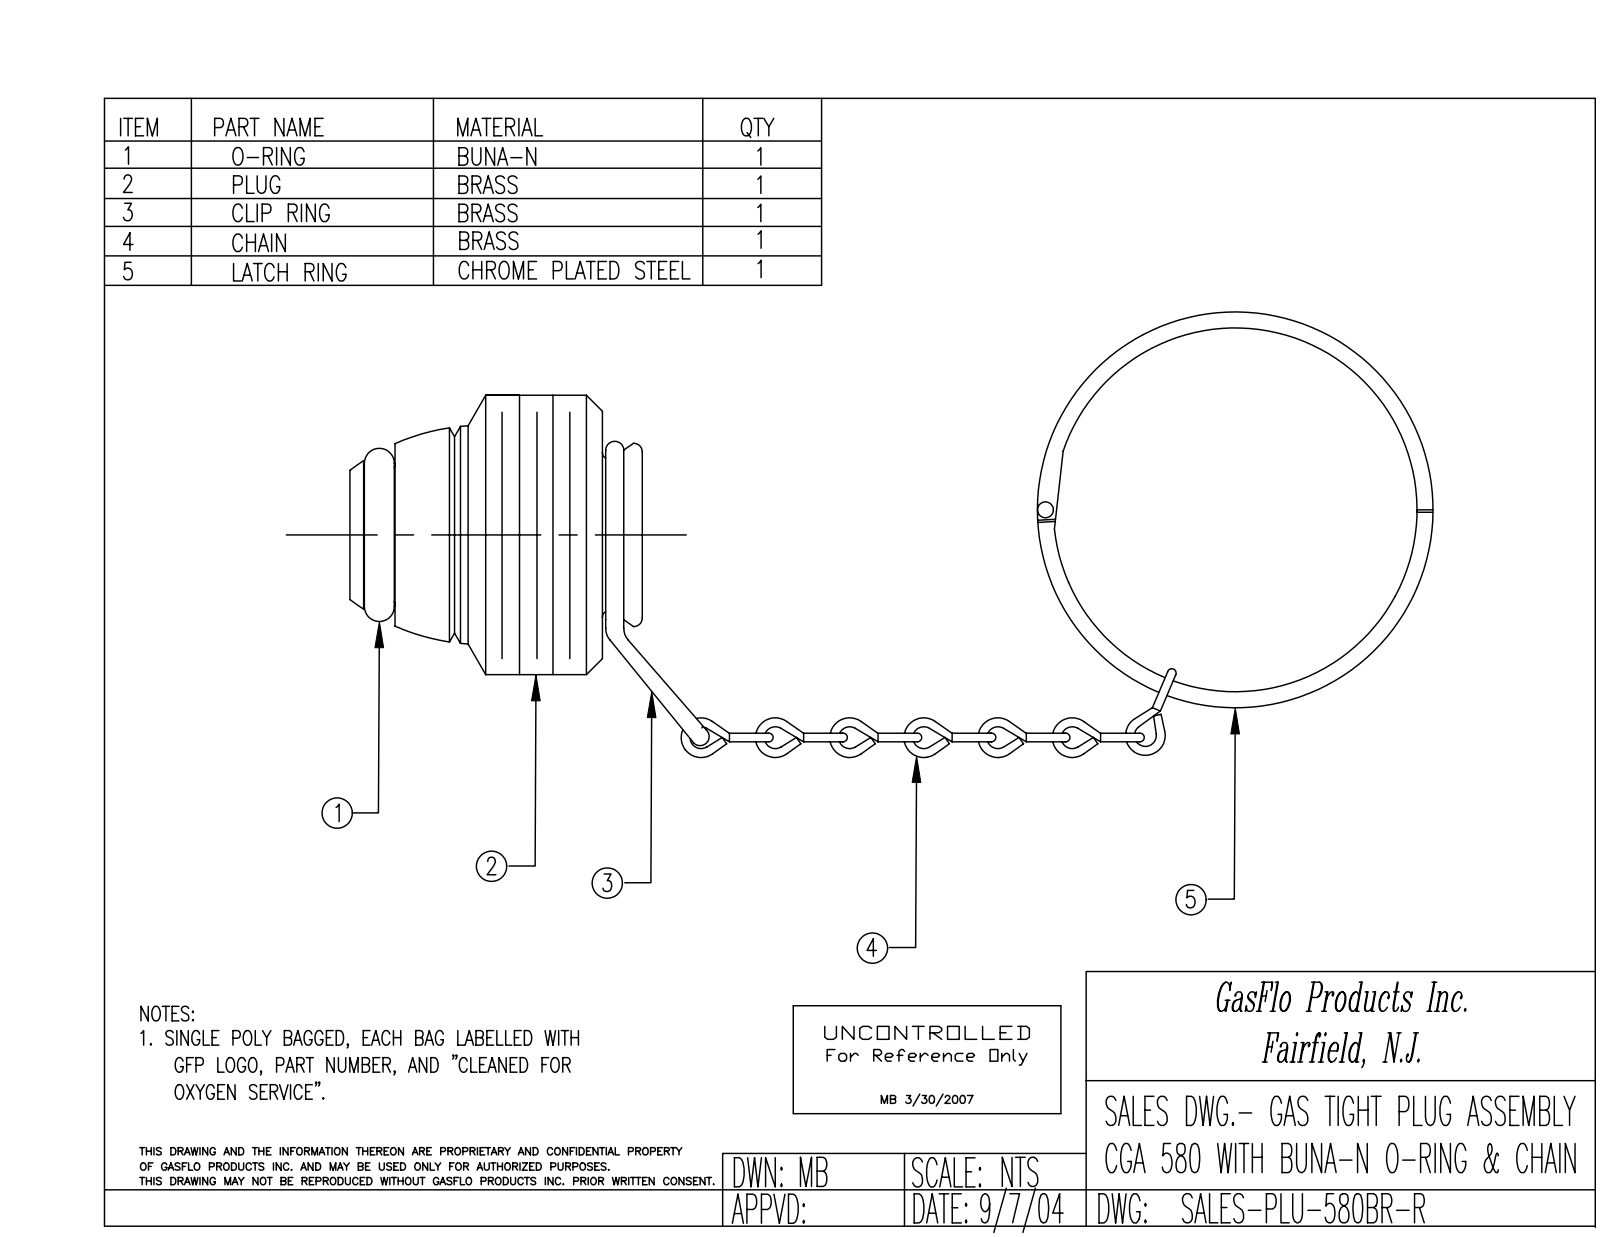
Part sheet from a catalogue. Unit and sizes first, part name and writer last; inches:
Units: inches
Overall size (bounding box): 5.304 × 2.163 × 0.958
Round holes (diameter × count): ⌀0.063 ×1, ⌀0.39 ×1
Round bosses / shafts (diameter × count): ⌀0.063 ×28, ⌀0.957 ×1, ⌀0.1 ×1
Partial cylindrical surfaces — rounded edges, fillets, slot ends (radius × count): R0.005 ×24, R0.25 ×4, R0.01 ×2
Main face-to-face distances: 0.815, 0.483, 0.332, 0.155, 0.328, 0.66, 0.377, 0.045, 1.002, 0.847
Volume: 0.456 in³ · Surface area: 9.496 in²
Bodies: 13 solids, 329 faces (61 planar, 112 cylindrical, 156 other)
Part name (STEP PRODUCT): ASY-000291; PRT-002239_BRASS; PRT-004033; PRT-002255_SMALL PIN (+5 more)
STEP written by: SolidWorks 2018 (CONFIG_CONTROL_DESIGN)
